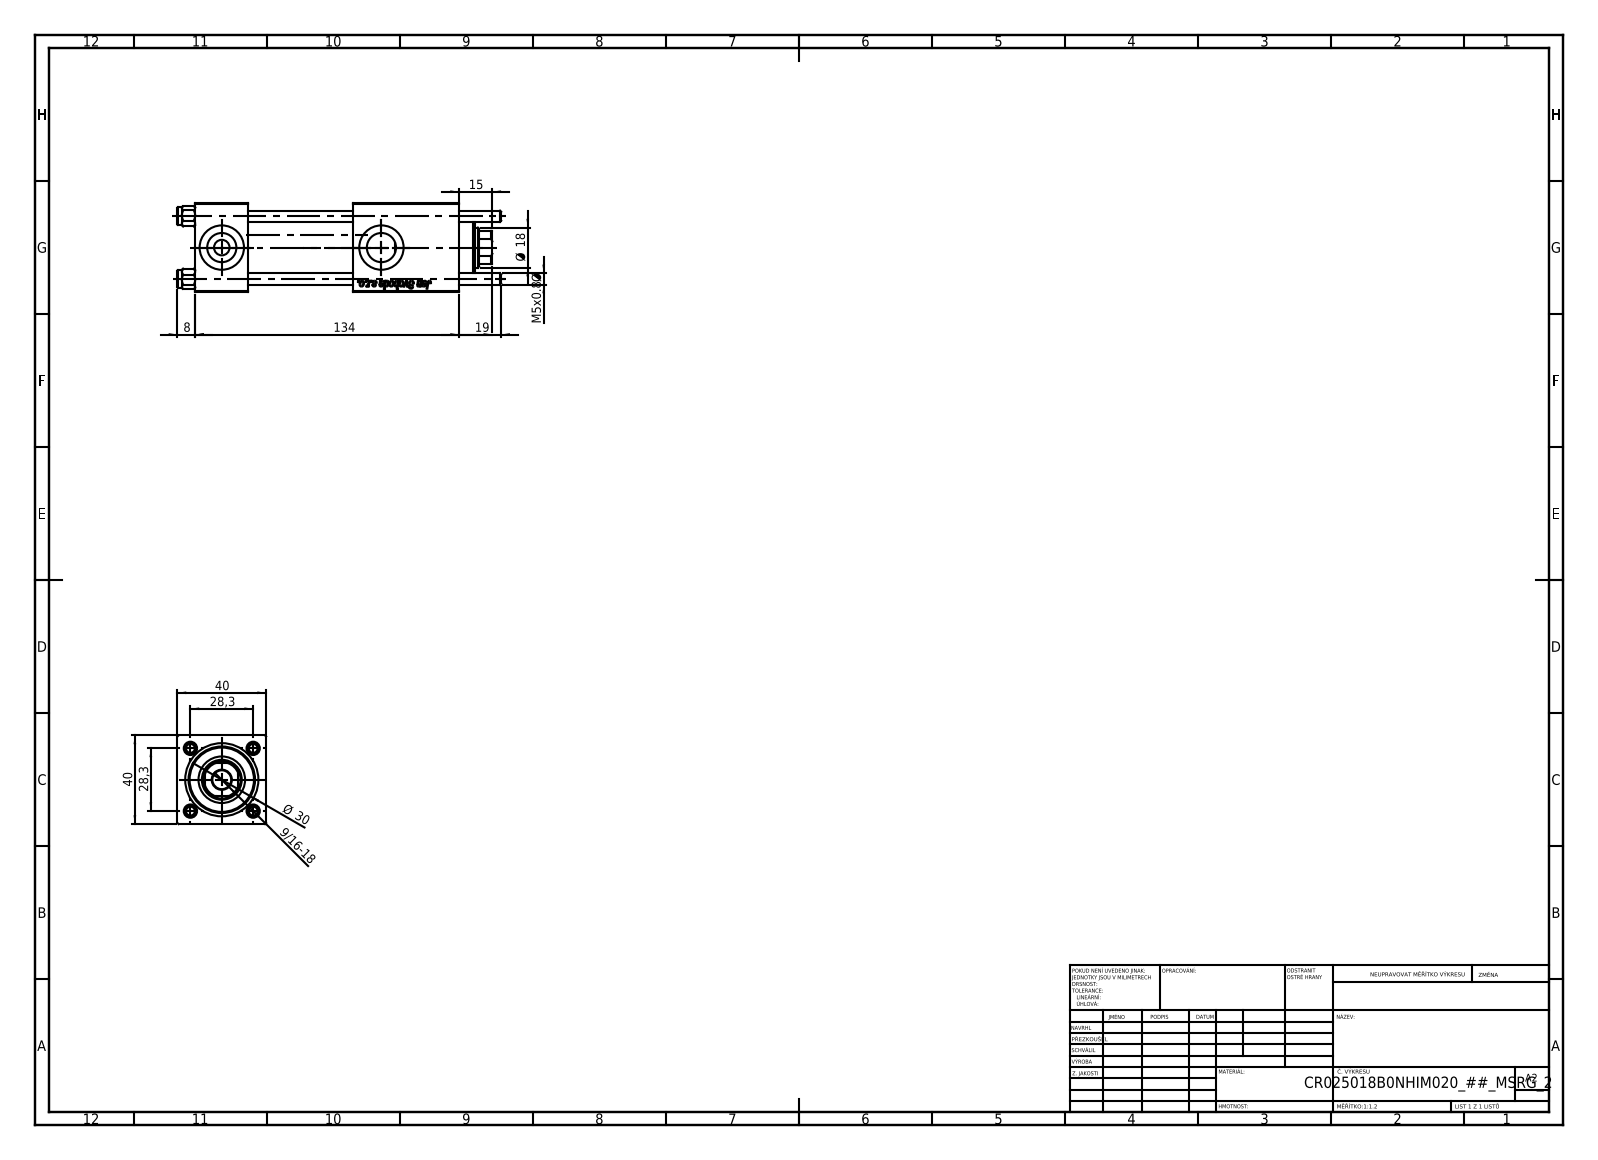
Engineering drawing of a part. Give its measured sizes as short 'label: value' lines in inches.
name: V215CR_VCP_B; NUT_M5_B; V215CR_B-1; V215_VC_A (+1 more)
written by: SolidWorks 2019 (CONFIG_CONTROL_DESIGN)
unit: in
bodies: 11 solids, 1152 faces (428 planar, 76 cylindrical, 648 other)
size: 5.748 × 1.575 × 1.575
volume: 9.306 in³; area: 94.39 in²
holes: 4× ⌀0.197, 3× ⌀0.787, 2× ⌀0.276, 2× ⌀0.518, 1× ⌀0.335, 1× ⌀0.709, 1× ⌀0.827, 1× ⌀0.984, 1× ⌀1.181
bosses: 4× ⌀0.315, 1× ⌀1.22
rounds: 1× R0.335
face distances: 1.575, 0.945, 2.795, 1.85, 3.555, 2.61, 0.76, 4.685, 3.74, 1.89
hole spacings: 0.788, 1.114, 1.576, 2.835
